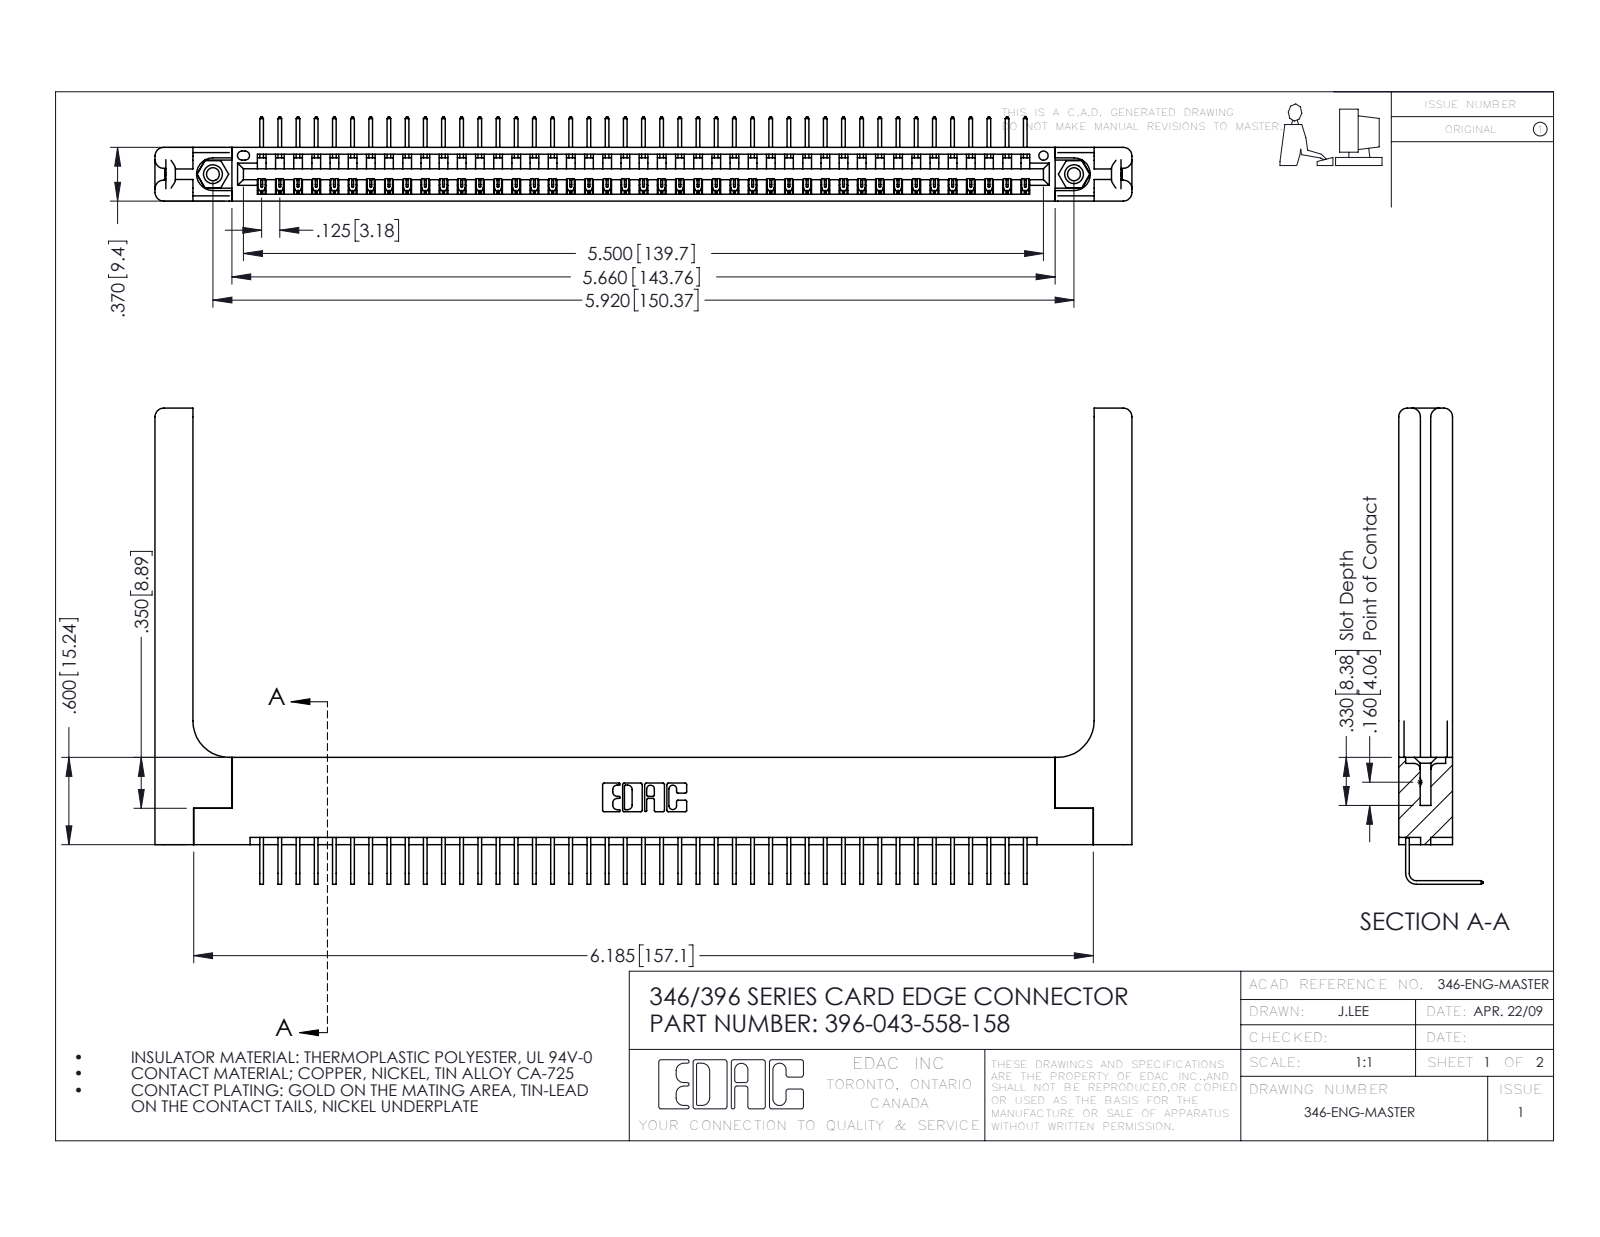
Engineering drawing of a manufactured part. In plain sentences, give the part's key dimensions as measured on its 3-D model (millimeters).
The part is named "345-250-001_345-250-001-102; 346 Part_Flush Mounting Lugs - 0.156 Dia-TH; 345-292-001_558 Tail - 2; 346-220-058_345-220-058 (+1 more)". Its 3-D file was written by "SolidWorks 2016 (CONFIG_CONTROL_DESIGN)". It is 48 solids with 2958 faces: 2030 planar, 868 cylindrical and 60 other. Overall it measures 170.6 by 83.1 by 14.7 millimeters. Its volume is 23 990 cubic millimeters and its surface area 26 630 square millimeters. Round holes: 2 of diameter 2.3, 2 of diameter 3.2, 2 of diameter 4, 1 of diameter 1.6. Round bosses or shafts: 2 of diameter 3.9. Partial cylindrical surfaces (rounded edges, fillets, slot ends): 86 of radius 0.2, 22 of radius 0.3, 16 of radius 1.5, 6 of radius 0.2, 6 of radius 0.8, 3 of radius 0.7, 2 of radius 0.8, 2 of radius 0.8. The main face-to-face distances are 9.4, 8.2, 1.2, 1.8, 3.8, 3.8, 0.6, 7.6, 6.4, 5.6. The hole center spacings are 6.2, 145.1, 150.4.
